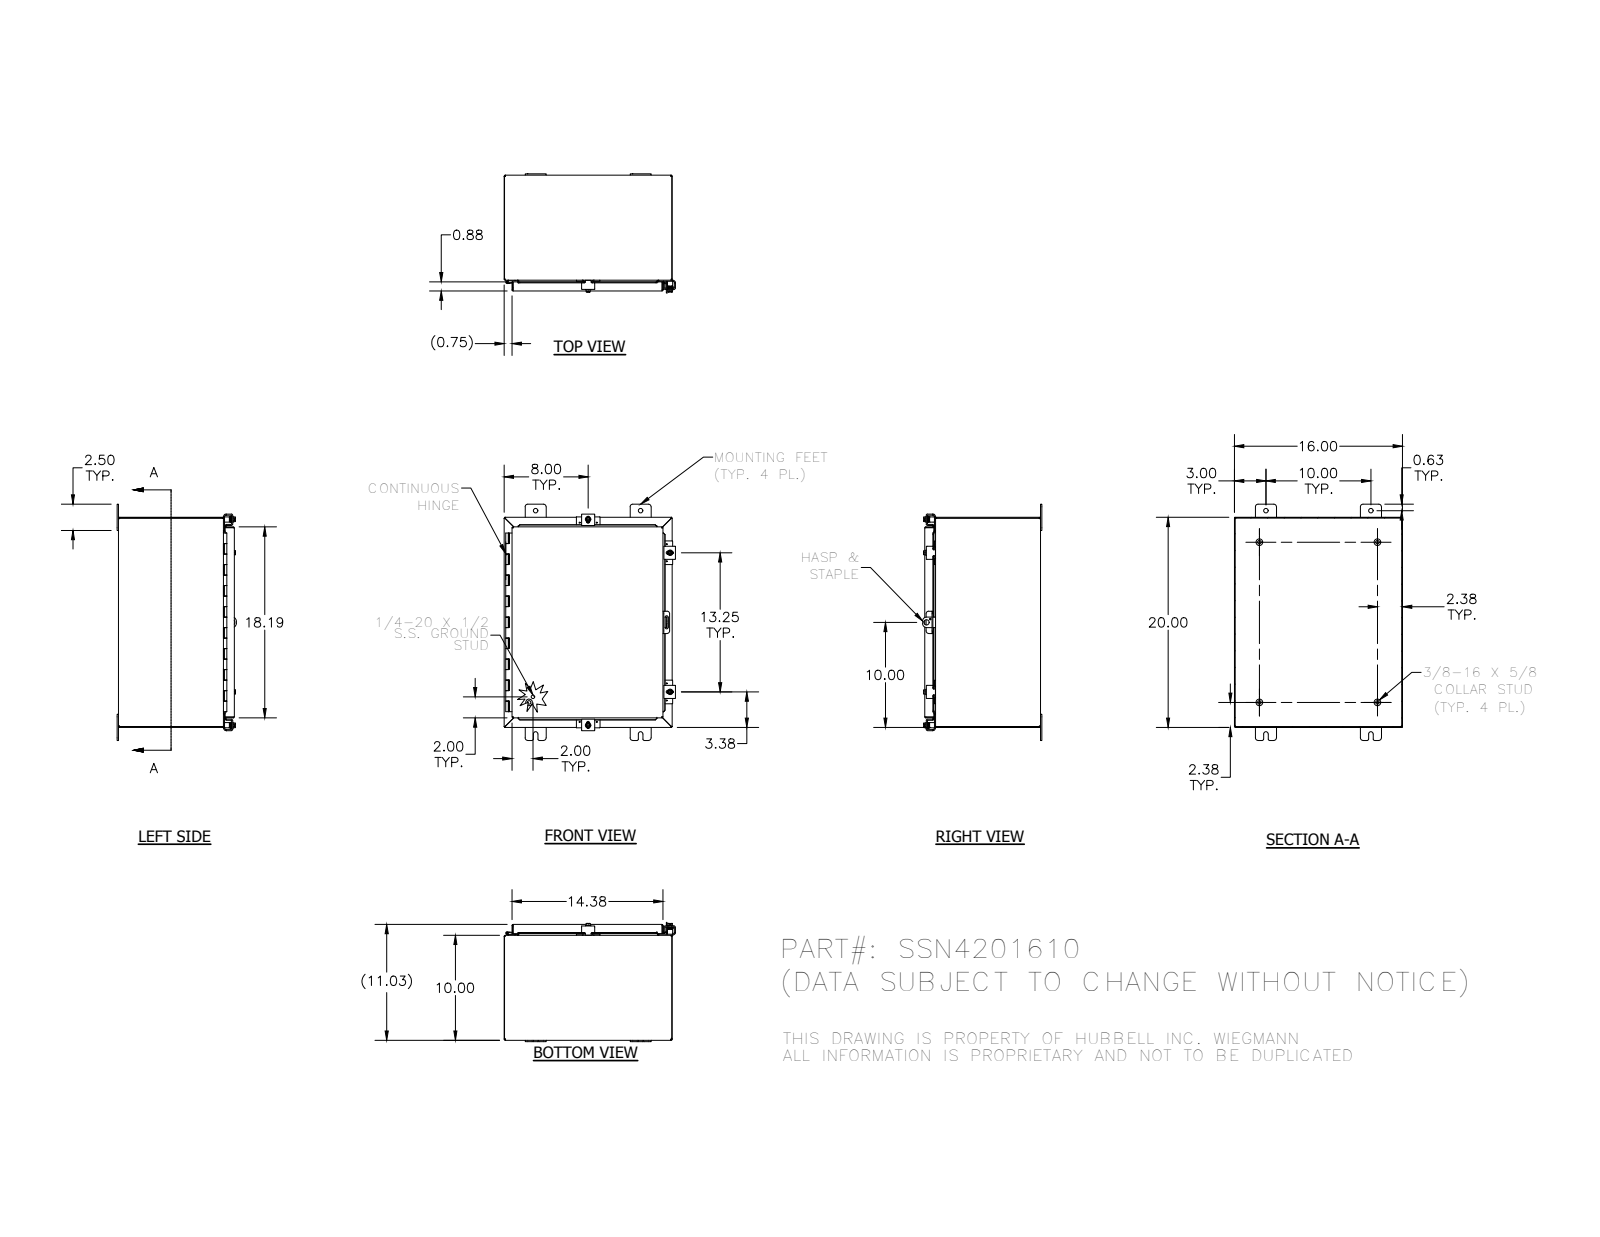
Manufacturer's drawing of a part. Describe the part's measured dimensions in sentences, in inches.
The part is named "SSN4201610BKP_1; 328137_1; 30824-1_1; 328137P_1 (+8 more)". Its 3-D file was written by "SolidWorks 2014 (AUTOMOTIVE_DESIGN)". It is 37 solids with 1444 faces: 567 planar, 632 cylindrical and 245 other. Overall it measures 22.5 by 16.311 by 11.355 inches. Its volume is 125.1 cubic inches and its surface area 3 280 square inches. Round holes: 8 of diameter 0.11, 4 of diameter 0.211, 4 of diameter 0.281, 4 of diameter 0.3, 4 of diameter 0.438, 1 of diameter 0.125, 1 of diameter 0.156, 1 of diameter 0.5. Round bosses or shafts: 6 of diameter 0.25, 4 of diameter 0.625, 4 of diameter 0.52, 4 of diameter 0.5, 4 of diameter 0.35, 4 of diameter 0.33, 2 of diameter 0.115, 1 of diameter 0.337. Partial cylindrical surfaces (rounded edges, fillets, slot ends): 49 of radius 0.03, 33 of radius 0.125, 29 of radius 0.25, 23 of radius 0.031, 23 of radius 0.105, 11 of radius 0.062, 8 of radius 0.07, 8 of radius 0.141. The main face-to-face distances are 0.074, 10.959, 15.926, 19.926, 10.885, 11.033, 15.852, 16, 9.926, 1.033. The hole center spacings are 0.876, 19.306, 13.25, 0.876, 1.625, 1.625, 4.189, 4.341.
